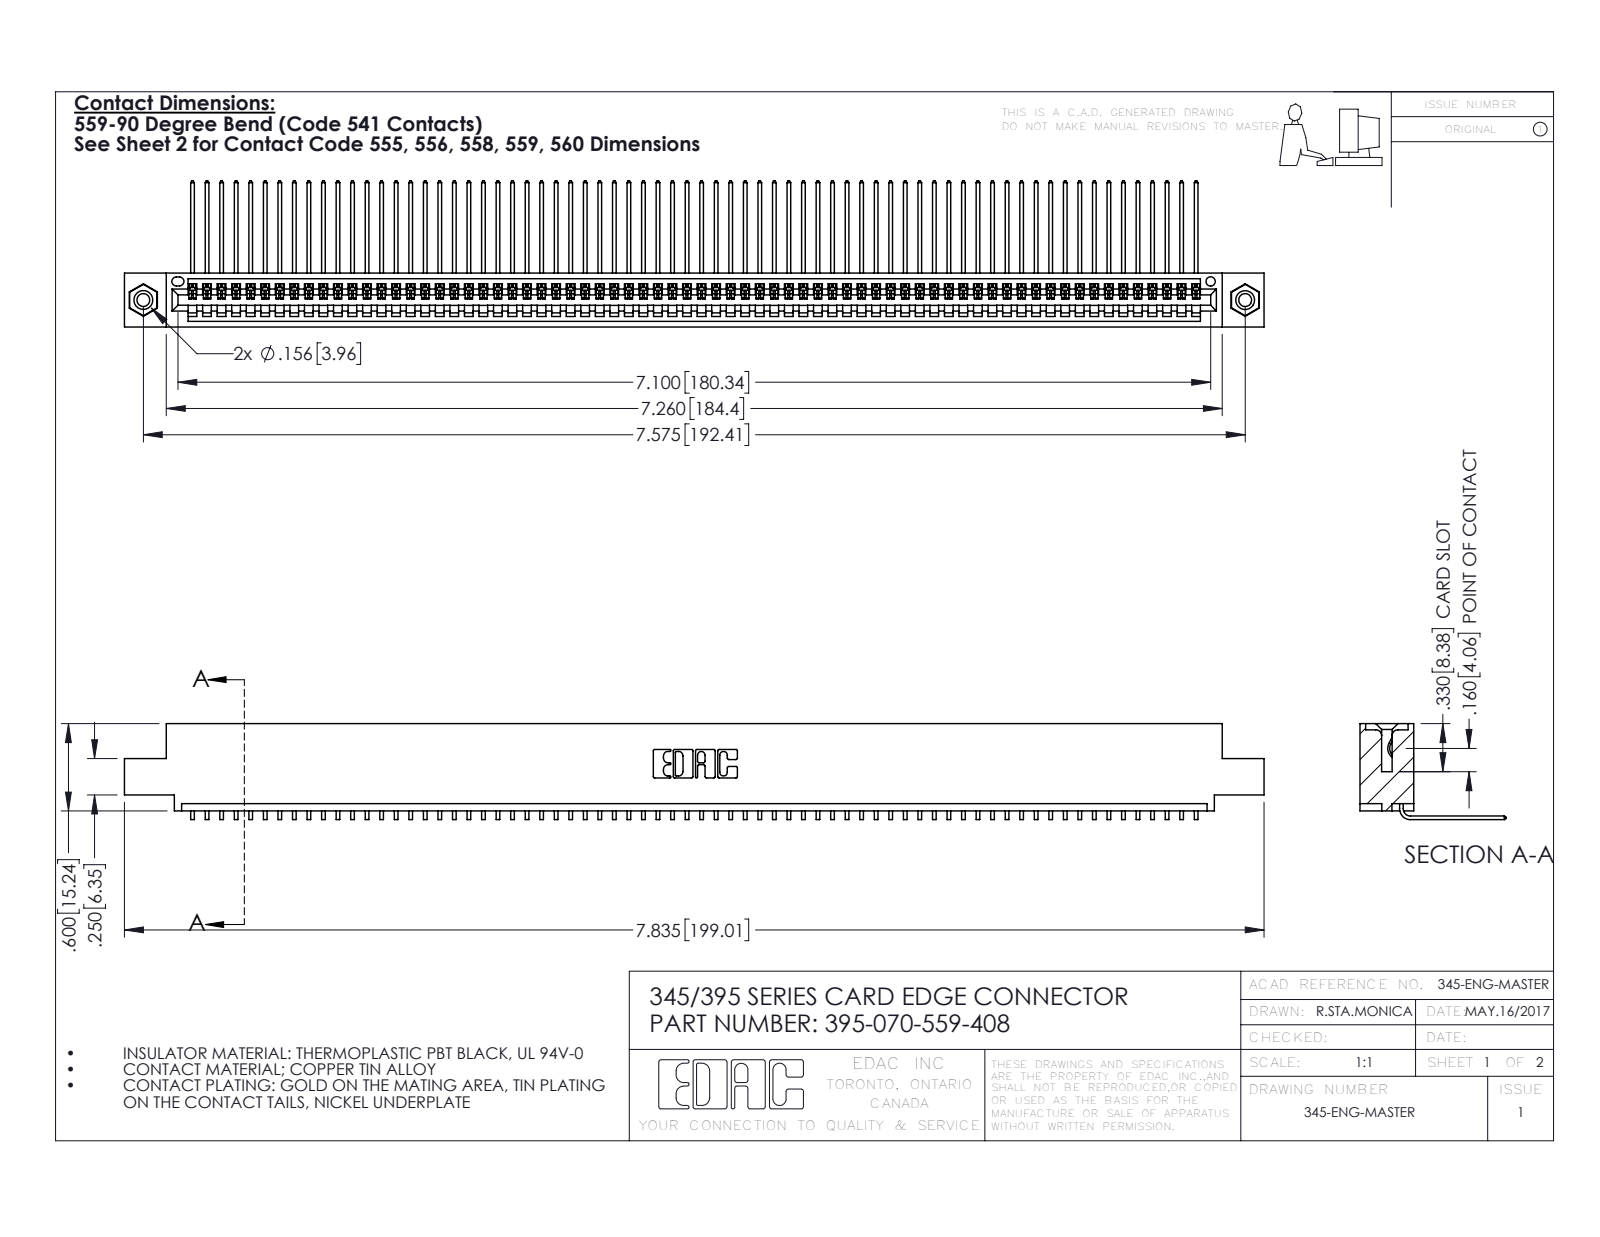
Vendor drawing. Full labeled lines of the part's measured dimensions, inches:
Part name (STEP PRODUCT): 345-250-001_345-250-003-102; 345-292-001_558 559 Tail - 1; 345 Part_0.110 Offset - 0.156 Dia-TI; 395-070-559-408
STEP written by: SolidWorks 2016 (CONFIG_CONTROL_DESIGN)
Units: inches
Bodies: 73 solids, 4390 faces (3056 planar, 1318 cylindrical, 16 other)
Overall size (bounding box): 7.835 × 1.005 × 0.659
Volume: 1.177 in³ · Surface area: 42.59 in²
Round holes (diameter × count): ⌀0.089 ×2, ⌀0.125 ×2, ⌀0.156 ×2, ⌀0.064 ×1
Round bosses / shafts (diameter × count): ⌀0.155 ×2
Partial cylindrical surfaces — rounded edges, fillets, slot ends (radius × count): R0.006 ×140, R0.01 ×22, R0.007 ×6, R0.031 ×6, R0.026 ×3, R0.031 ×2, R0.04 ×2, R0.014 ×1
Main face-to-face distances: 0.072, 0.298, 0.37, 0.2, 0.098, 0.272, 0.025, 0.225, 0.149, 0.072
Hole centre spacings: 0.27, 7.339, 7.575
